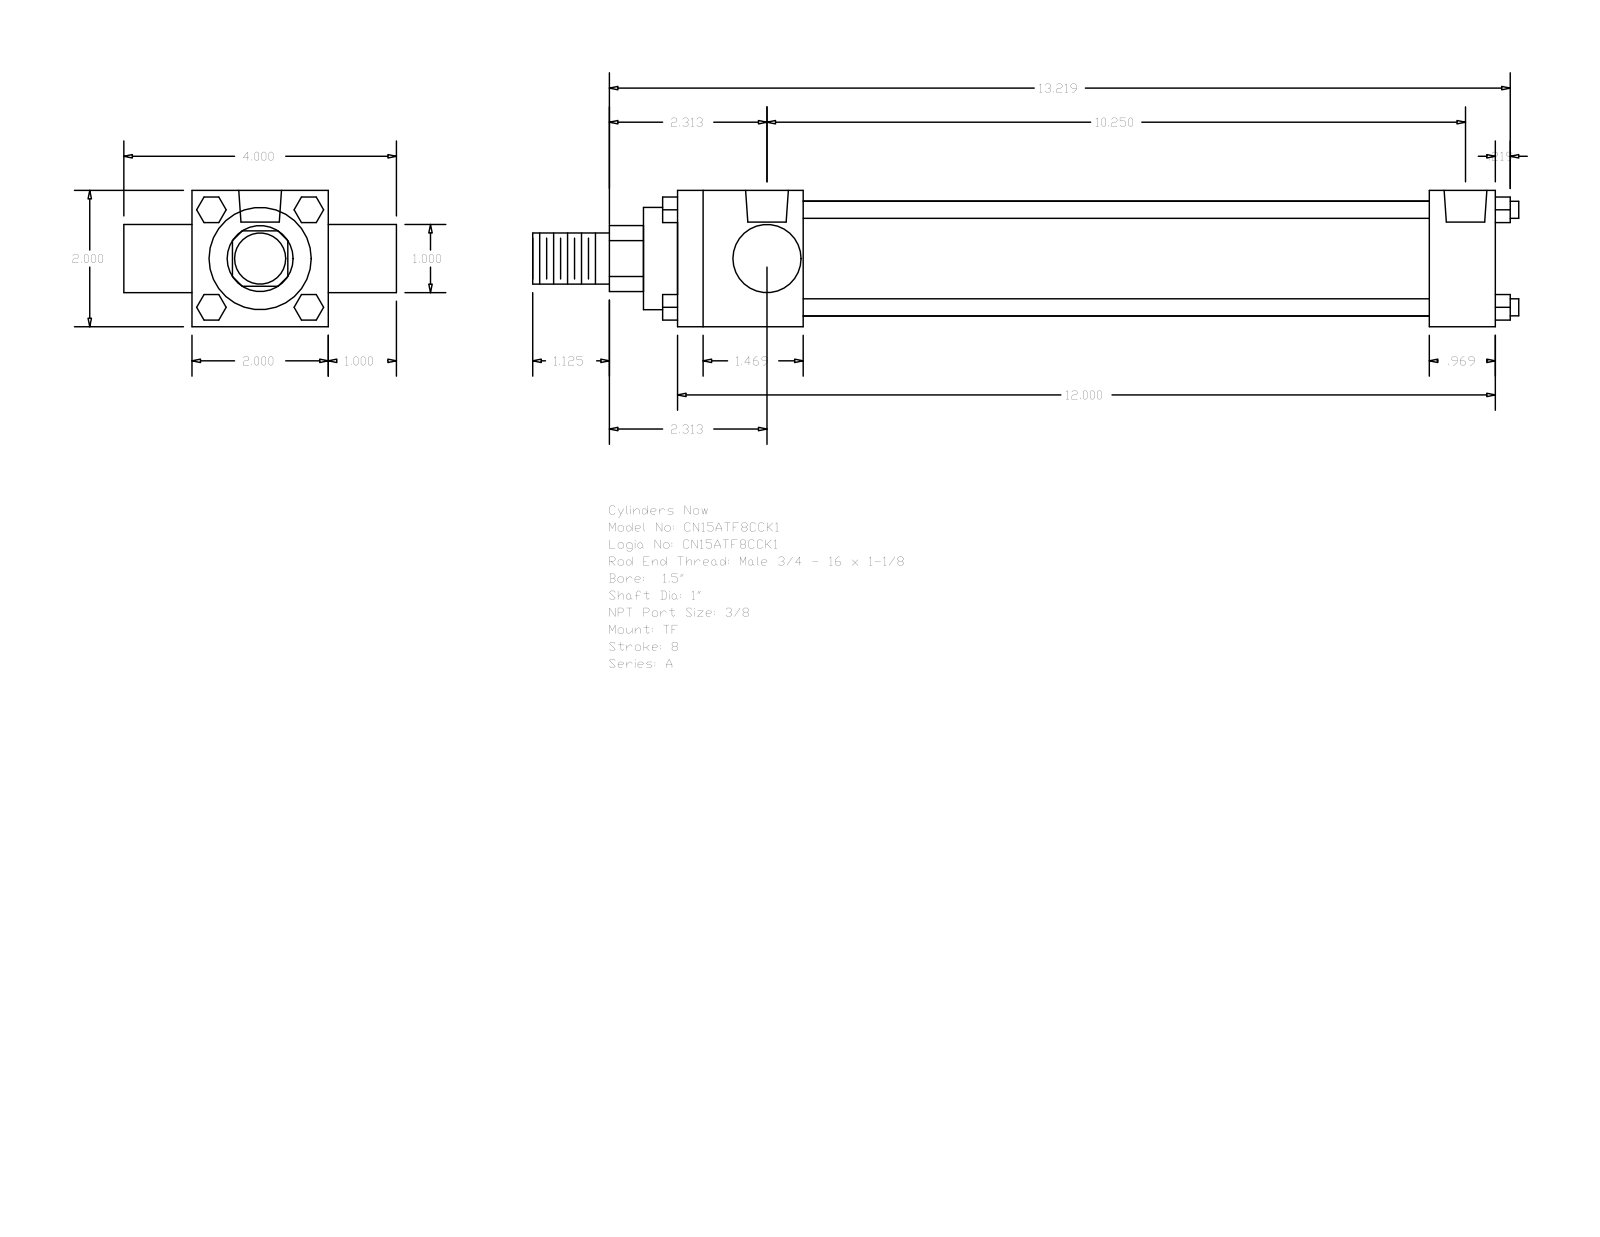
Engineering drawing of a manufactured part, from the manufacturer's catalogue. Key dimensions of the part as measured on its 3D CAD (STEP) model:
Part name (STEP PRODUCT): A_TF__0150_1
STEP written by: GSSL Pune (CONFIG_CONTROL_DESIGN)
Units: millimetres
Bodies: 0 solids, 120 faces (92 planar, 28 cylindrical, 0 other)
Overall size (bounding box): 367.51 × 101.6 × 50.8
Round holes (diameter × count): ⌀5.56 ×3, ⌀15.93 ×2
Round bosses / shafts (diameter × count): ⌀6.35 ×4, ⌀25.4 ×2, ⌀42.93 ×1, ⌀38.1 ×1, ⌀19.05 ×1
Partial cylindrical surfaces — rounded edges, fillets, slot ends (radius × count): R12.29 ×1
Main face-to-face distances: 50.8, 25.4, 304.8, 76.2, 46.83, 280.19, 233.36, 257.97, 24.61, 12.7
Hole centre spacings: 3.97, 256.38, 252.41, 260.35
